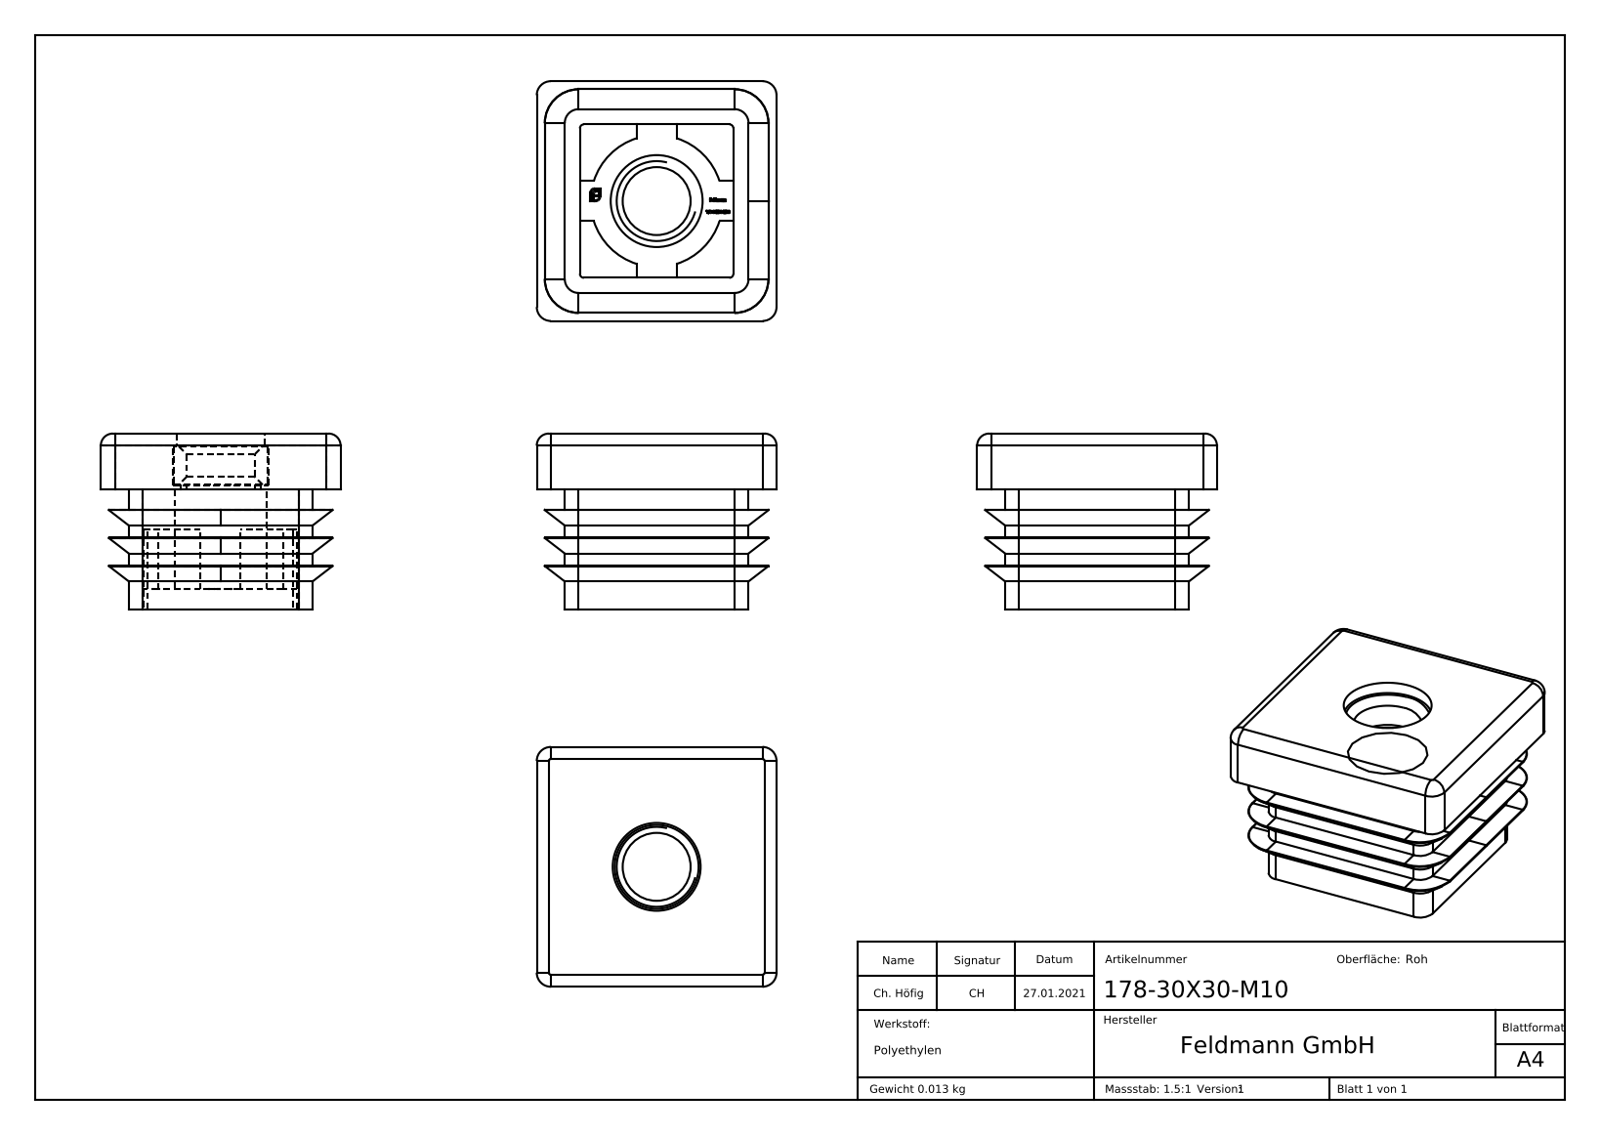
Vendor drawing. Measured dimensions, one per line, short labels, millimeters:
name: 178-30X30-M10
written by: SolidWorks 2018 (CONFIG_CONTROL_DESIGN)
unit: mm
bodies: 2 solids, 498 faces (256 planar, 70 cylindrical, 172 other)
size: 30 × 30 × 22
volume: 11 175 mm³; area: 7 183 mm²
holes: 1× ⌀8.5, 1× ⌀11, 1× ⌀11.5
rounds: 8× R1.75, 4× R0.5, 4× R1.5, 1× R8.25
face distances: 3.5, 7, 5.4, 26.5, 24.6, 1.9, 21.1, 5.5, 9, 2.5
